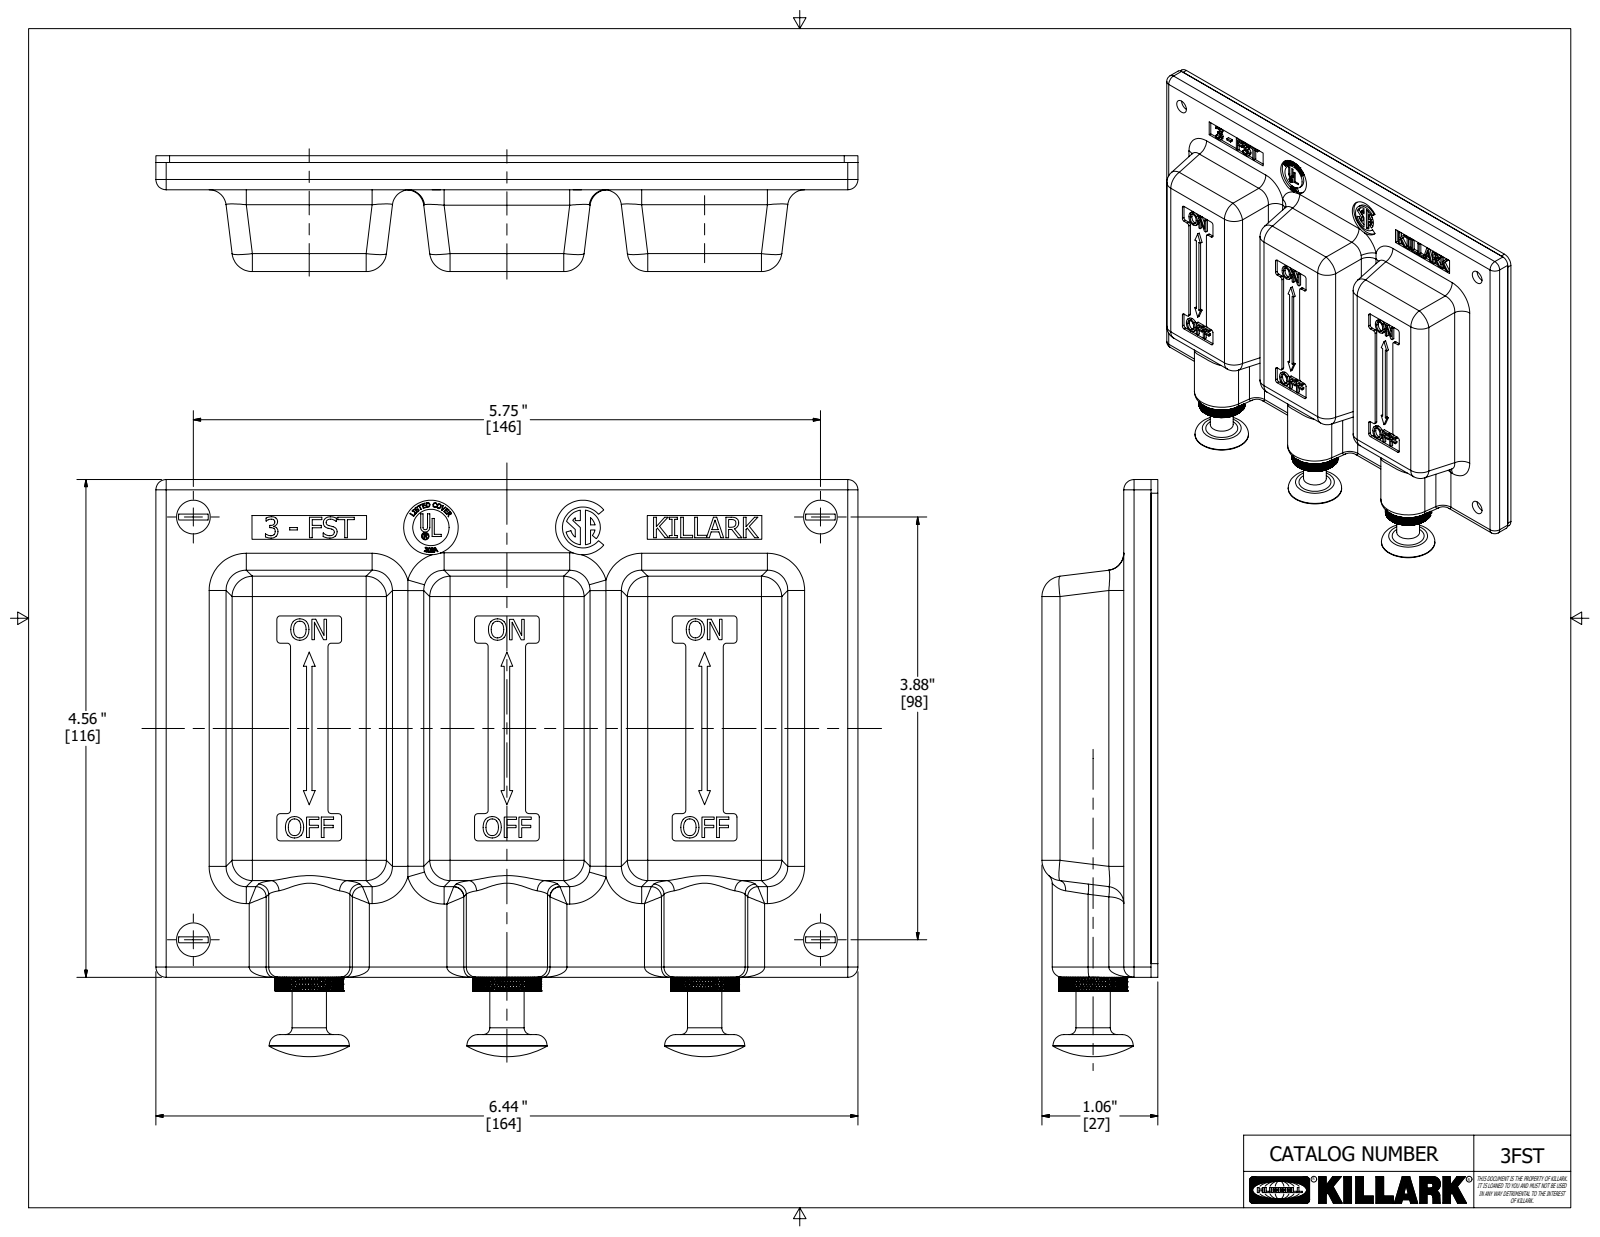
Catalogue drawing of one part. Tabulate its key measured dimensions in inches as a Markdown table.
| quantity | value |
| --- | --- |
| part name | 02877CAAM; 0067662M; 0301475B; 0722675B (+4 more) |
| STEP written by | Autodesk Inventor 2020 (AUTOMOTIVE_DESIGN) |
| units | inches |
| bodies | 21 solids, 10571 faces (8073 planar, 1850 cylindrical, 648 other) |
| overall size | 6.438 × 5.291 × 1.43 |
| volume | 8.866 in³ |
| surface area | 147.5 in² |
| round holes (diameter × count) | 0.156 × 7, 0.187 × 4, 0.22 × 3, 0.313 × 3, 0.324 × 3, 0.332 × 3, 0.422 × 3, 0.453 × 3, 0.5 × 1 |
| round bosses / shafts (diameter × count) | 0.164 × 4, 0.734 × 3, 0.625 × 3, 0.496 × 3, 0.437 × 3, 0.314 × 3, 0.213 × 3, 0.333 × 1 |
| partial cylindrical surfaces (radius × count) | 0.094 × 41, 0.031 × 36, 0.187 × 32, 0.047 × 14, 0.125 × 13, 0.156 × 12, 0.281 × 8, 0.25 × 6 |
| main face-to-face distances | 0.75, 0.125, 0.25, 0.063, 0.313, 0.139, 0.625, 0.875, 0.937, 1 |
| hole center spacings | 1.813, 1.813, 3.875, 5.75, 6.933, 1.812, 1.813, 2.18 |
